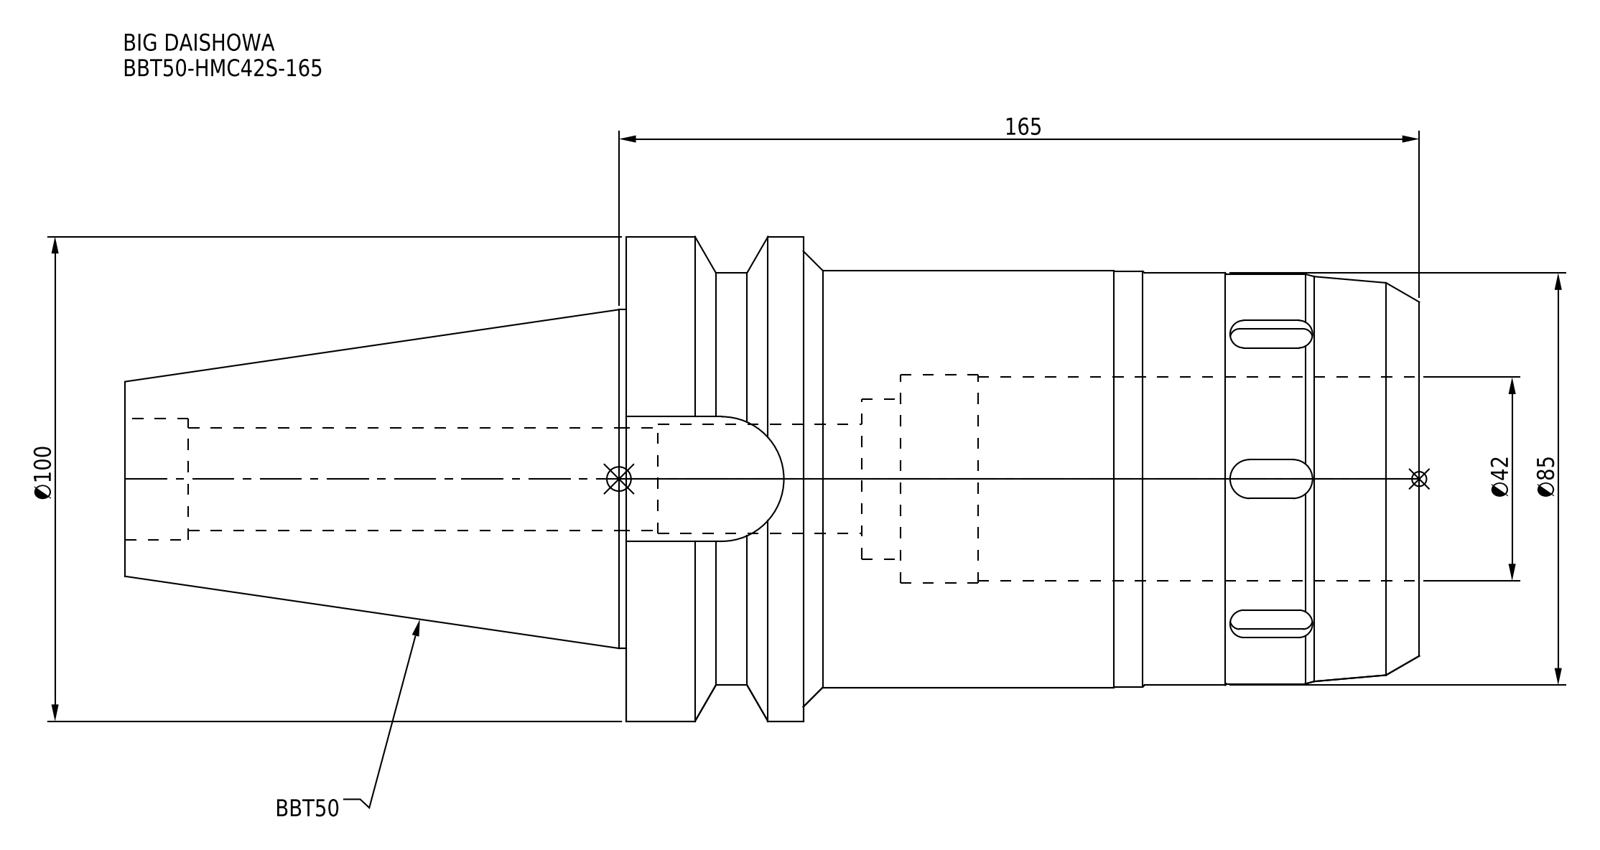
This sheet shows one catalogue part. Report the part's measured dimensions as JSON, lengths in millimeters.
{"part_name": "BBT50-HMC42S-165", "step_written_by": "CREO PARAMETRIC BY PTC INC, 2016380 (AUTOMOTIVE_DESIGN)", "units": "millimeters", "bodies": {"solids": 1, "faces": 104, "planar": 40, "cylindrical": 46, "other": 18}, "overall_size": [266.8, 100, 100], "volume_mm3": 1002000, "surface_area_mm2": 102882, "round_holes": [[21.2, 1], [22.5, 1], [25, 1], [33, 1], [42, 1], [43, 1]], "round_bosses_or_shafts": [[100, 1], [86, 1], [85.7, 1], [85, 1], [84.5, 1], [69.85, 1]], "partial_cylinders_radius": [[4, 12], [12.85, 1]], "face_to_face_distances": [163.5, 127, 36.5, 266.8, 139.8, 103.3, 70.8, 8, 107, 20]}
